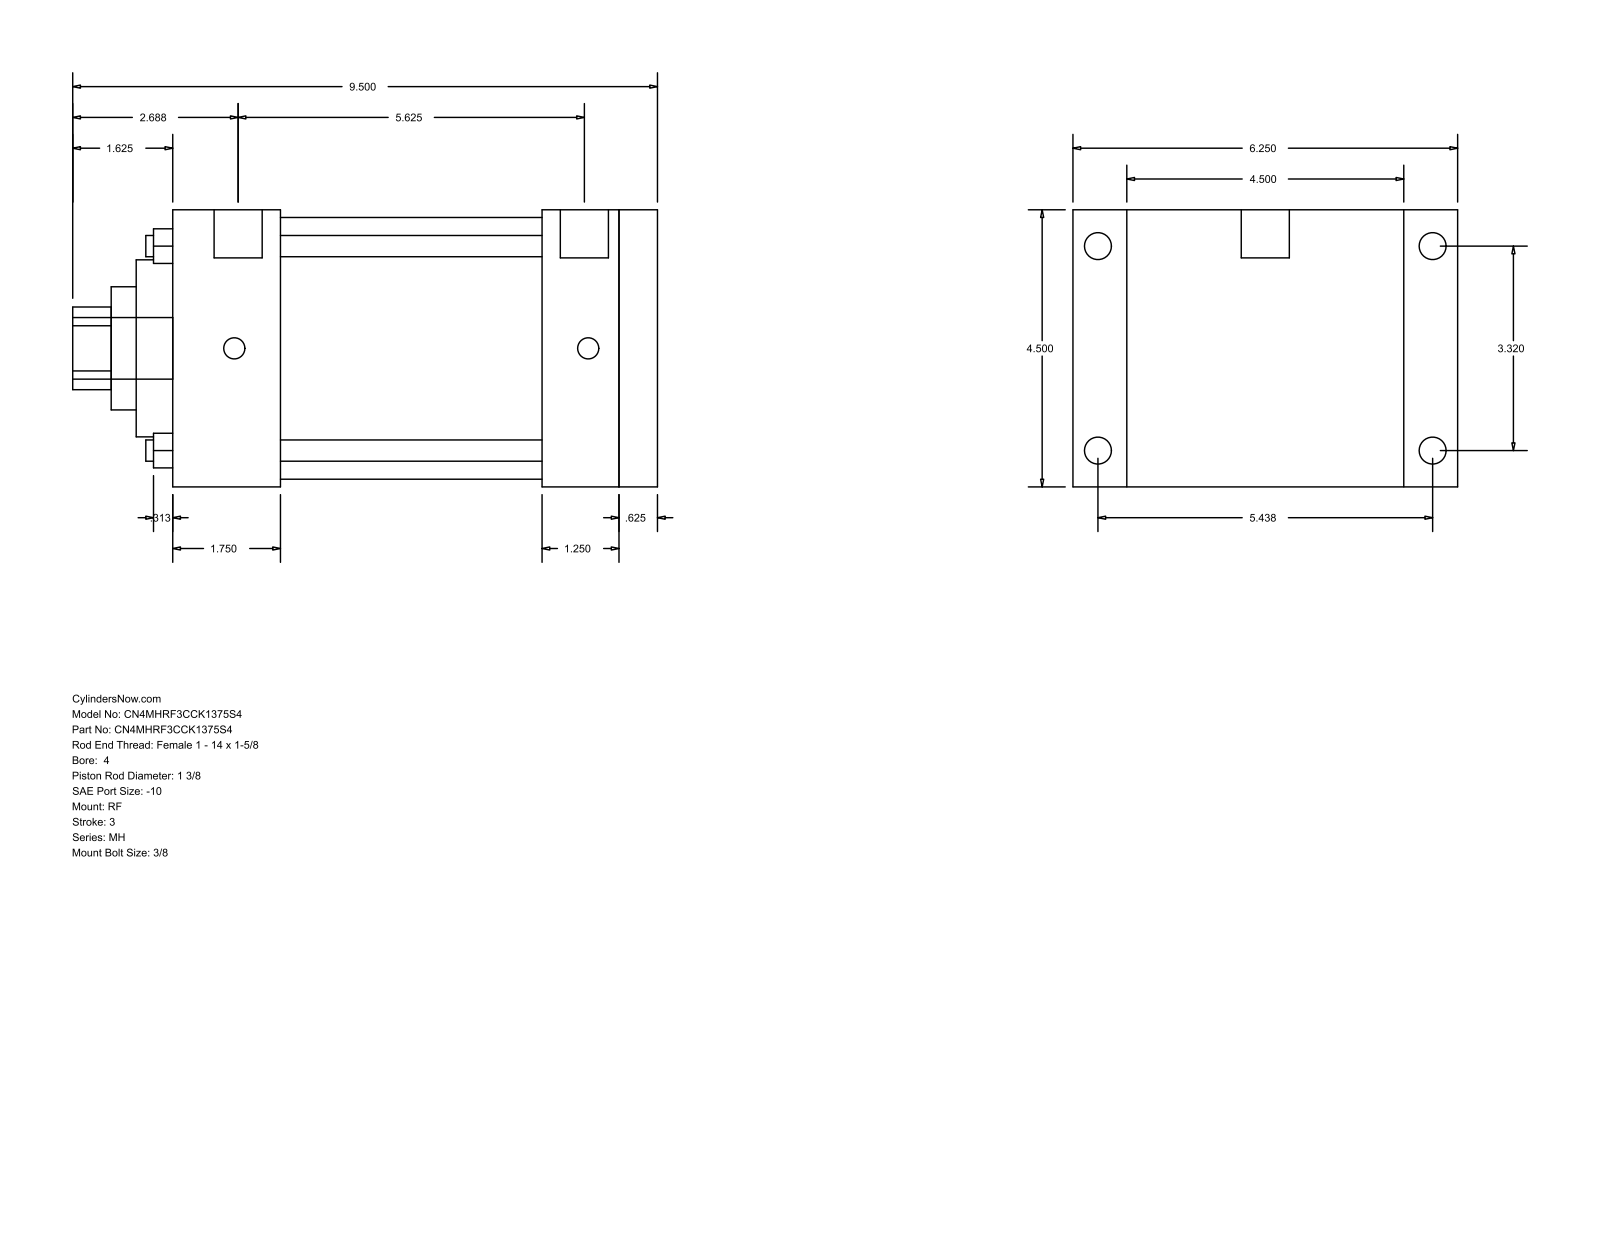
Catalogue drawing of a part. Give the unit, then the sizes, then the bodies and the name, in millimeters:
Units: millimetres
Overall size (bounding box): 241.3 × 158.75 × 114.3
Round holes (diameter × count): ⌀8.76 ×4, ⌀34.92 ×1, ⌀50.8 ×1, ⌀73.03 ×1, ⌀107.95 ×1
Round bosses / shafts (diameter × count): ⌀11.13 ×4, ⌀8.73 ×4, ⌀19.84 ×2, ⌀25.4 ×1
Partial cylindrical surfaces — rounded edges, fillets, slot ends (radius × count): R17.06 ×1
Main face-to-face distances: 114.3, 200.03, 184.16, 15.87, 44.45, 139.71, 155.58, 152.41, 107.96, 31.75
Hole centre spacings: 59.62, 84.32, 119.25
Bodies: 0 solids, 94 faces (65 planar, 29 cylindrical, 0 other)
Part name (STEP PRODUCT): MH_RF__0400_1.375
STEP written by: GSSL Pune (CONFIG_CONTROL_DESIGN)
